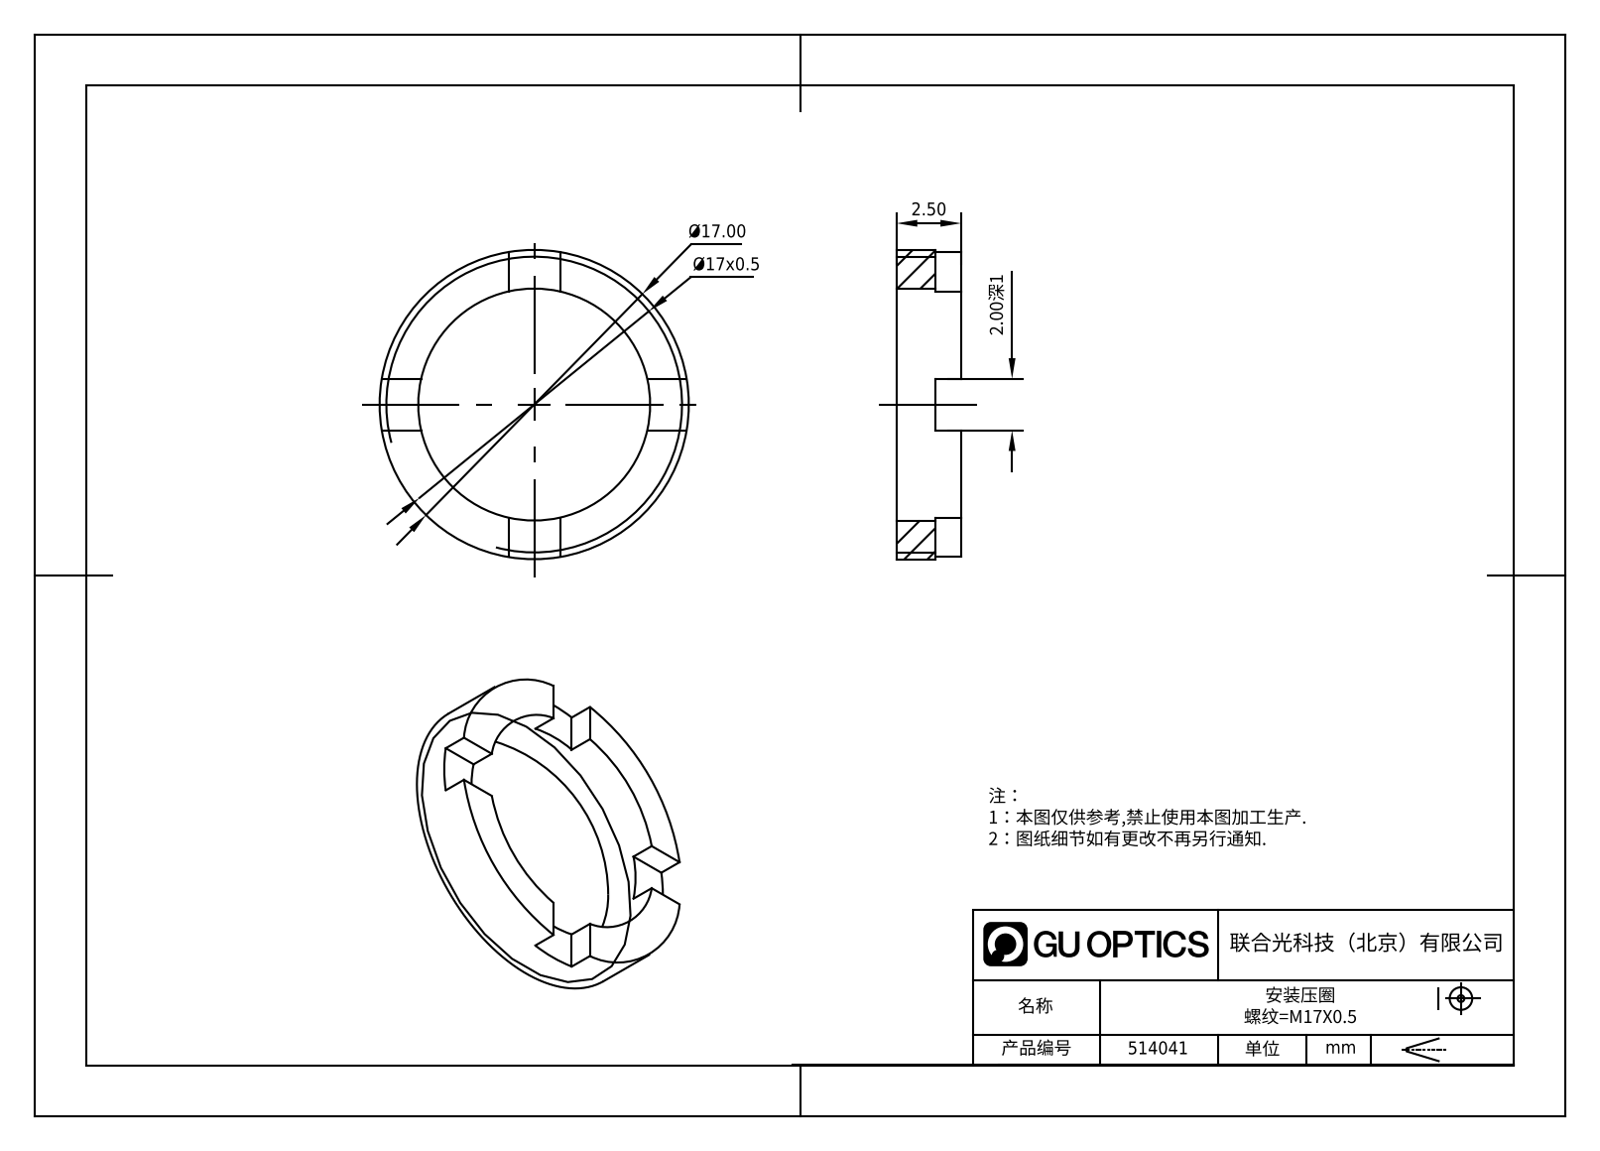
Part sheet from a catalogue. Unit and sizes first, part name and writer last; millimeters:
Units: millimetres
Overall size (bounding box): 17 × 17 × 2.5
Round holes (diameter × count): ⌀14 ×1
Round bosses / shafts (diameter × count): ⌀17 ×1
Main face-to-face distances: 2.5, 1.5, 1, 2
Volume: 171 mm³ · Surface area: 386 mm²
Bodies: 1 solid, 21 faces (17 planar, 4 cylindrical, 0 other)
Part name (STEP PRODUCT): 514041
STEP written by: SolidWorks 2020 (CONFIG_CONTROL_DESIGN)
